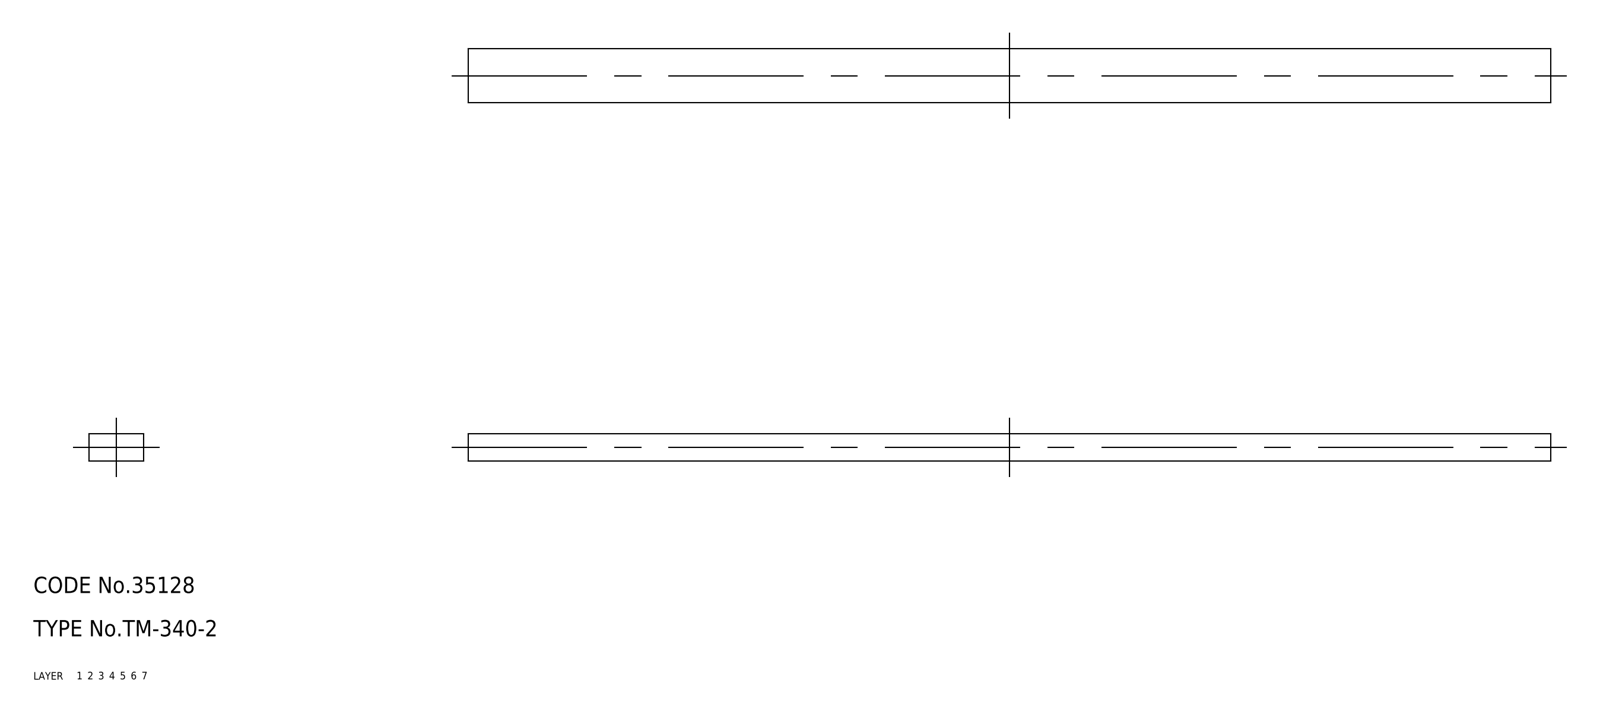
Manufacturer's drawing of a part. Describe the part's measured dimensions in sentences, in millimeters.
The part is named "rubber foam; TM_340_2". Its 3-D file was written by "SolidWorks 2015 (AUTOMOTIVE_DESIGN)". It is 1 solid with 6 faces: 6 planar, 0 cylindrical and 0 other. Overall it measures 200 by 10 by 5 millimeters. Its volume is 10 000 cubic millimeters and its surface area 6 100 square millimeters. The main face-to-face distances are 5, 10, 200.
